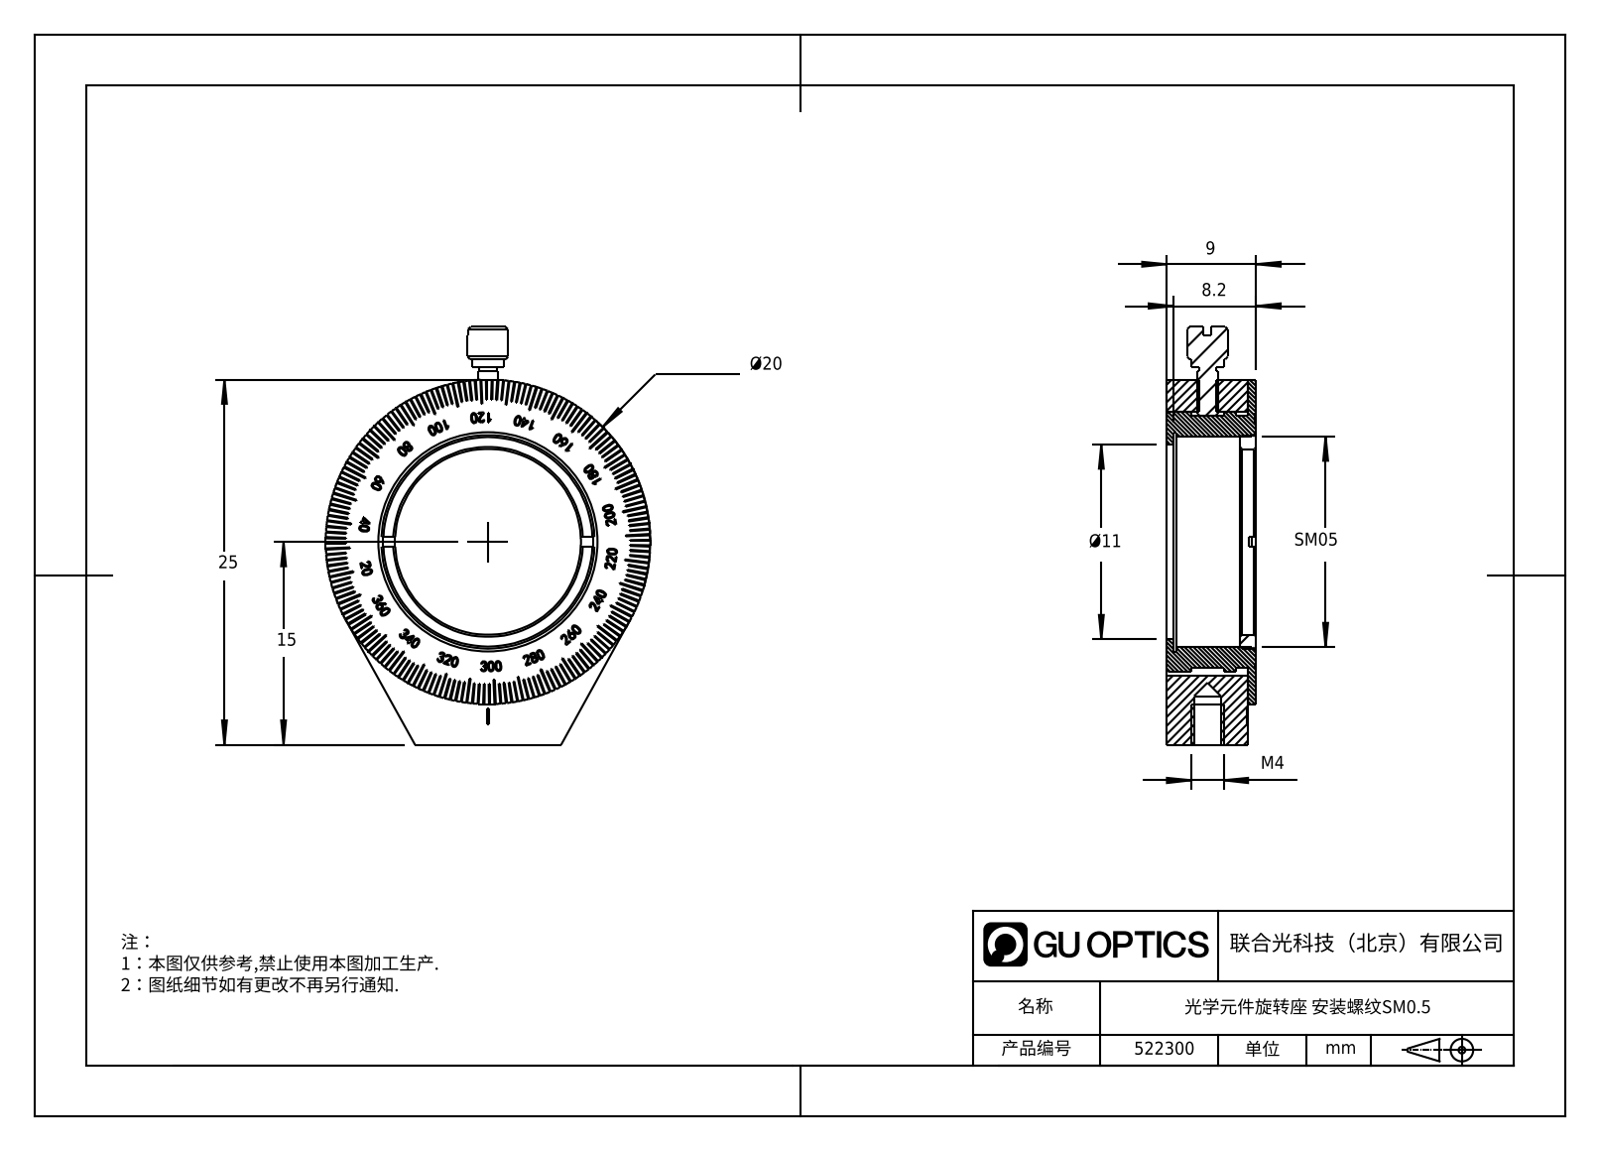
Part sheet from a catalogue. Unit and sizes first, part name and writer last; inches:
Units: inches
Overall size (bounding box): 1.243 × 0.787 × 0.354
Round holes (diameter × count): ⌀0.081 ×1, ⌀0.13 ×1, ⌀0.433 ×1, ⌀0.512 ×1
Round bosses / shafts (diameter × count): ⌀0.787 ×1, ⌀0.591 ×1, ⌀0.551 ×1, ⌀0.535 ×1, ⌀0.197 ×1, ⌀0.157 ×1, ⌀0.098 ×1, ⌀0.083 ×1
Partial cylindrical surfaces — rounded edges, fillets, slot ends (radius × count): R0.256 ×1
Main face-to-face distances: 0.315, 0.039, 0.354, 0.079, 0.276, 0.031, 0.283, 0.323, 0.236, 0.244
Volume: 0.146 in³ · Surface area: 5.106 in²
Bodies: 4 solids, 1227 faces (992 planar, 37 cylindrical, 198 other)
STEP written by: SolidWorks 2021 (CONFIG_CONTROL_DESIGN)
